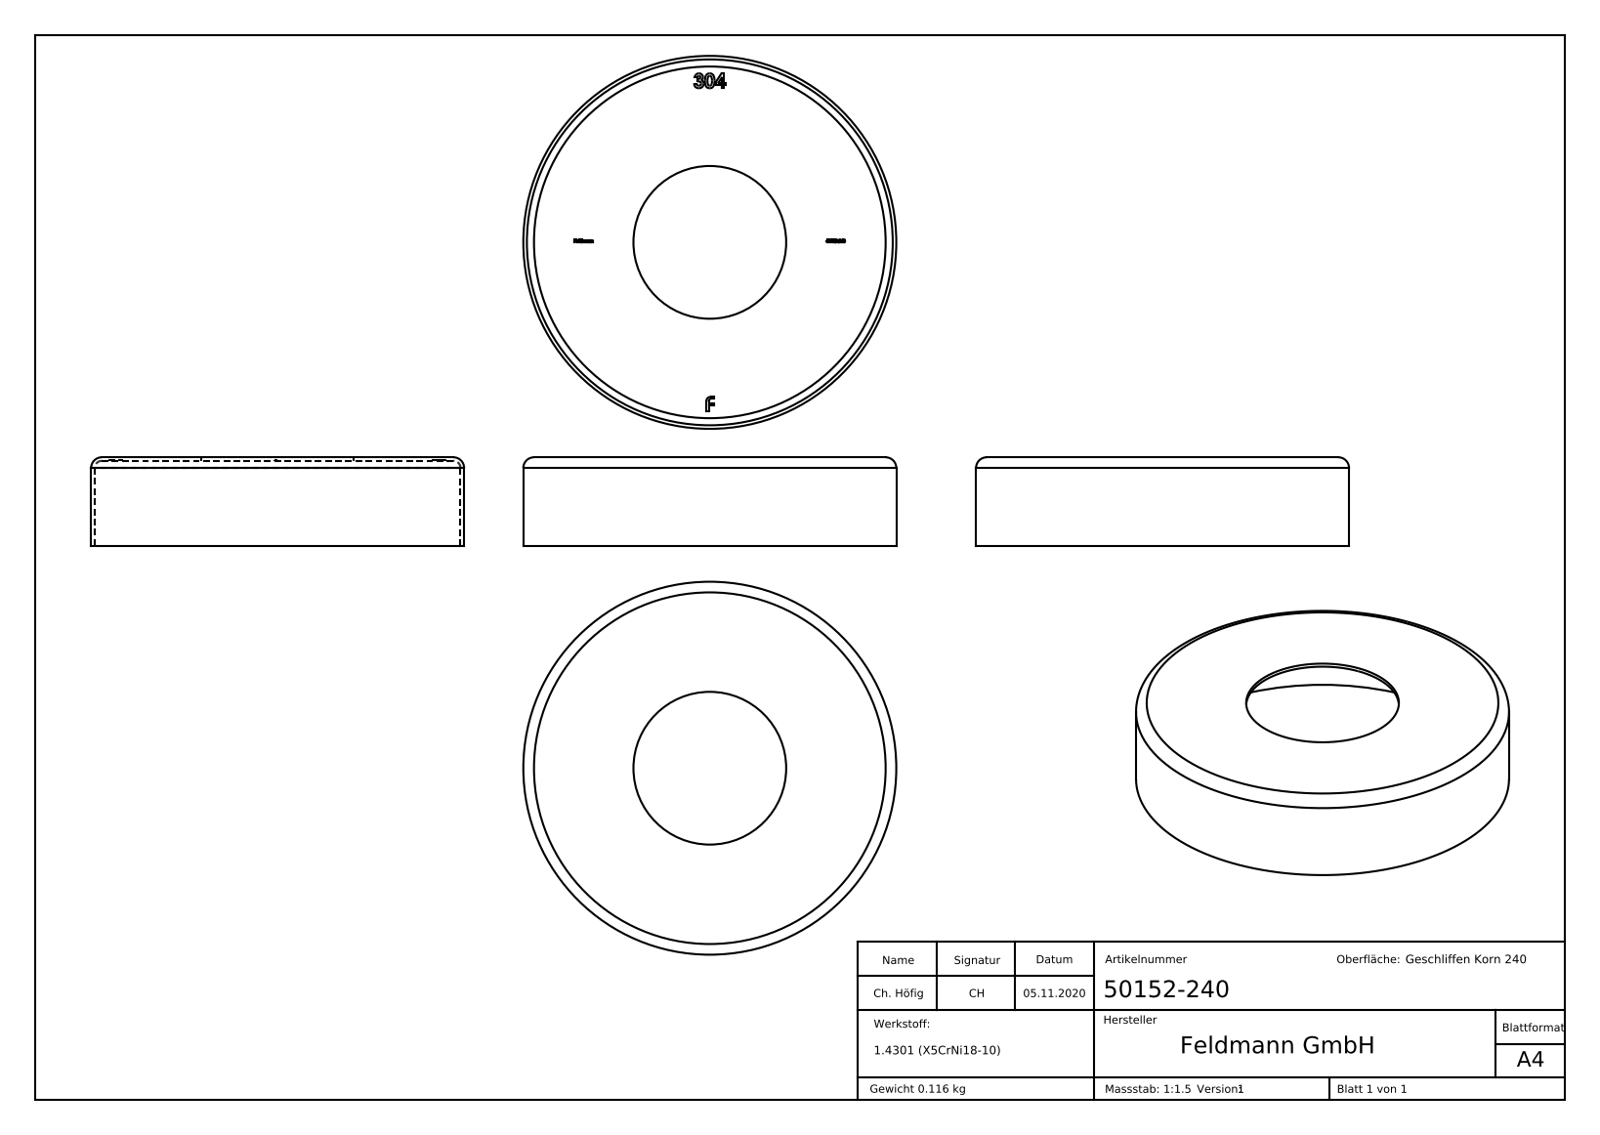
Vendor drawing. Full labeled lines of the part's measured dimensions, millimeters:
Part name (STEP PRODUCT): 50152-240
STEP written by: SolidWorks 2018 (CONFIG_CONTROL_DESIGN)
Units: millimetres
Bodies: 1 solid, 289 faces (160 planar, 6 cylindrical, 123 other)
Overall size (bounding box): 105 × 105 × 25
Volume: 14 692 mm³ · Surface area: 29 865 mm²
Round holes (diameter × count): ⌀43 ×1, ⌀103 ×1
Round bosses / shafts (diameter × count): ⌀105 ×1
Main face-to-face distances: 1, 24, 25, 24.1, 0.9, 0.71, 5, 4.29, 0.58, 0.69
